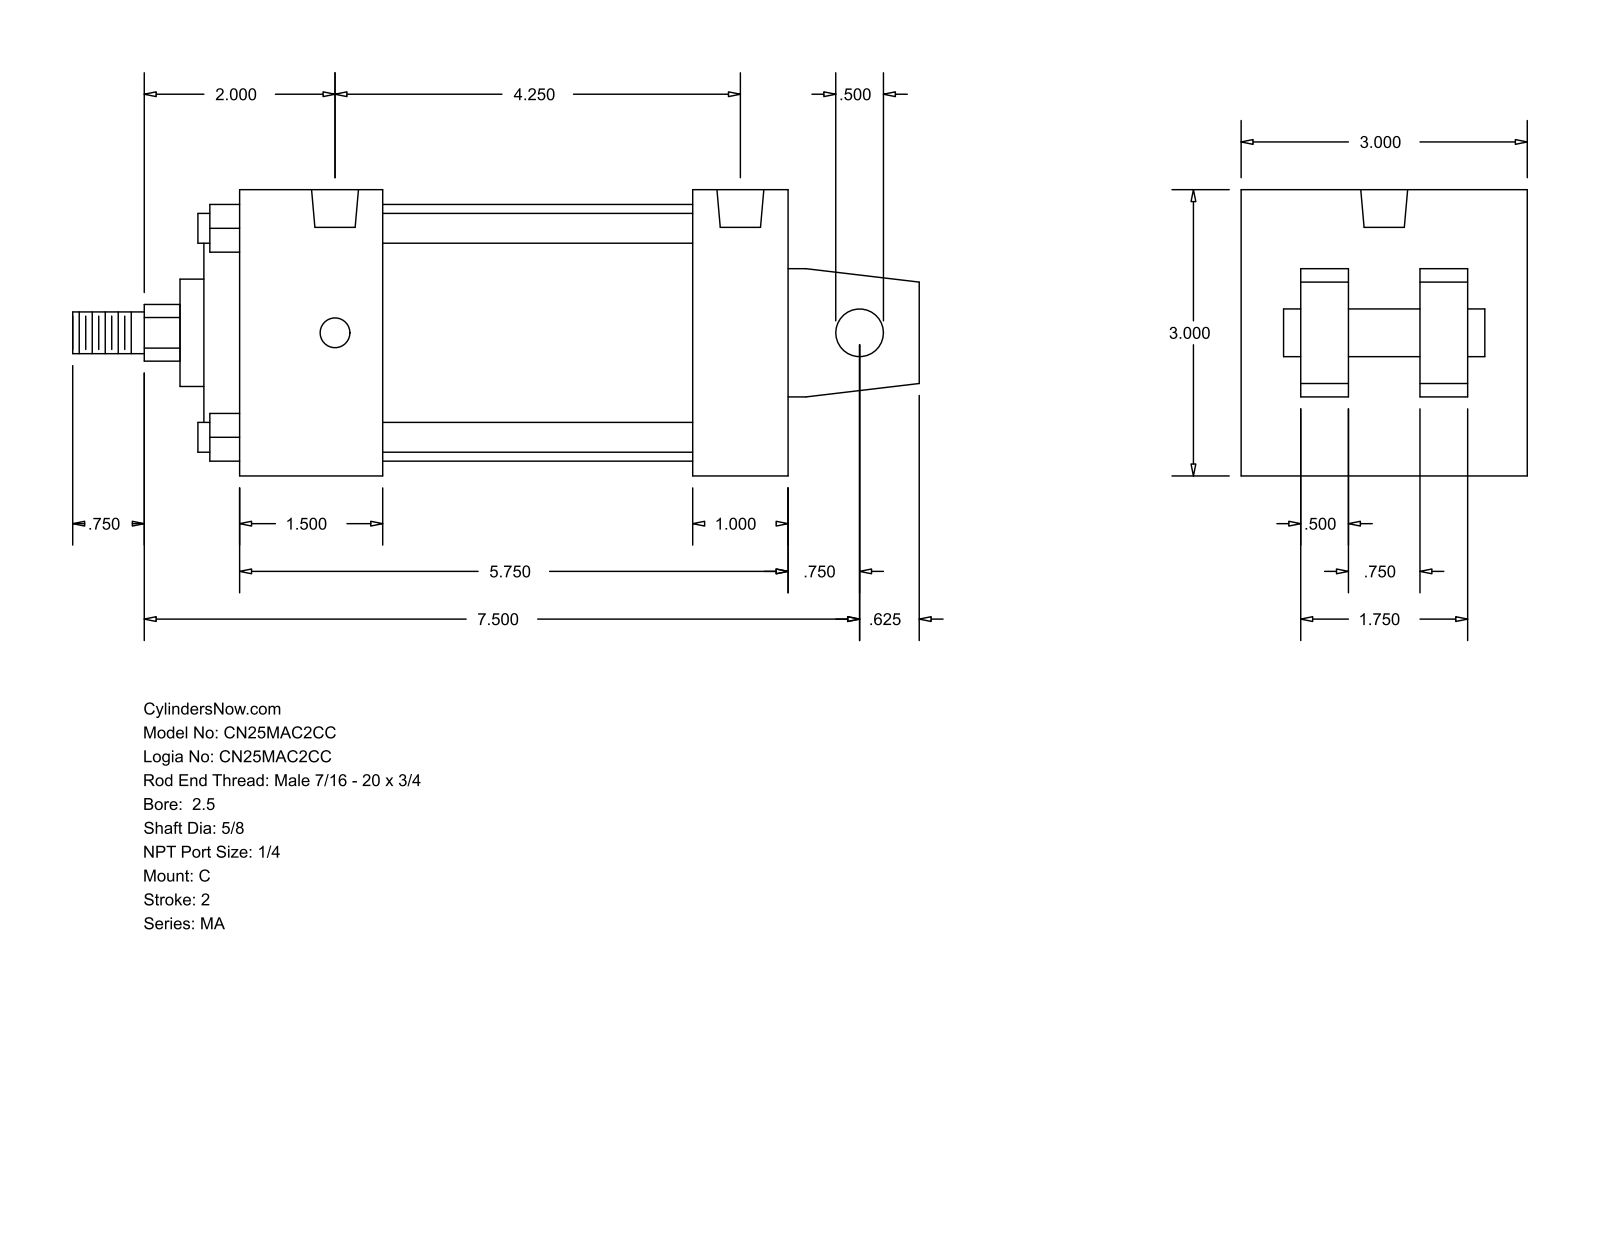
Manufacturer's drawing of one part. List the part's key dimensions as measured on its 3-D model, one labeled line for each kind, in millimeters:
Part name (STEP PRODUCT): MA_C__0250_0.625
STEP written by: GSSL Pune (CONFIG_CONTROL_DESIGN)
Units: millimetres
Bodies: 0 solids, 105 faces (77 planar, 28 cylindrical, 0 other)
Overall size (bounding box): 225.43 × 76.2 × 76.2
Round holes (diameter × count): ⌀7.94 ×4, ⌀12.49 ×2
Round bosses / shafts (diameter × count): ⌀7.94 ×4, ⌀68.33 ×1, ⌀50.8 ×1, ⌀28.57 ×1, ⌀15.88 ×1, ⌀12.7 ×1, ⌀11.11 ×1
Partial cylindrical surfaces — rounded edges, fillets, slot ends (radius × count): R7.54 ×1
Main face-to-face distances: 76.2, 146.05, 12.7, 15.87, 60.33, 47.63, 25.4, 82.55, 38.1, 120.65
Hole centre spacings: 107.95
